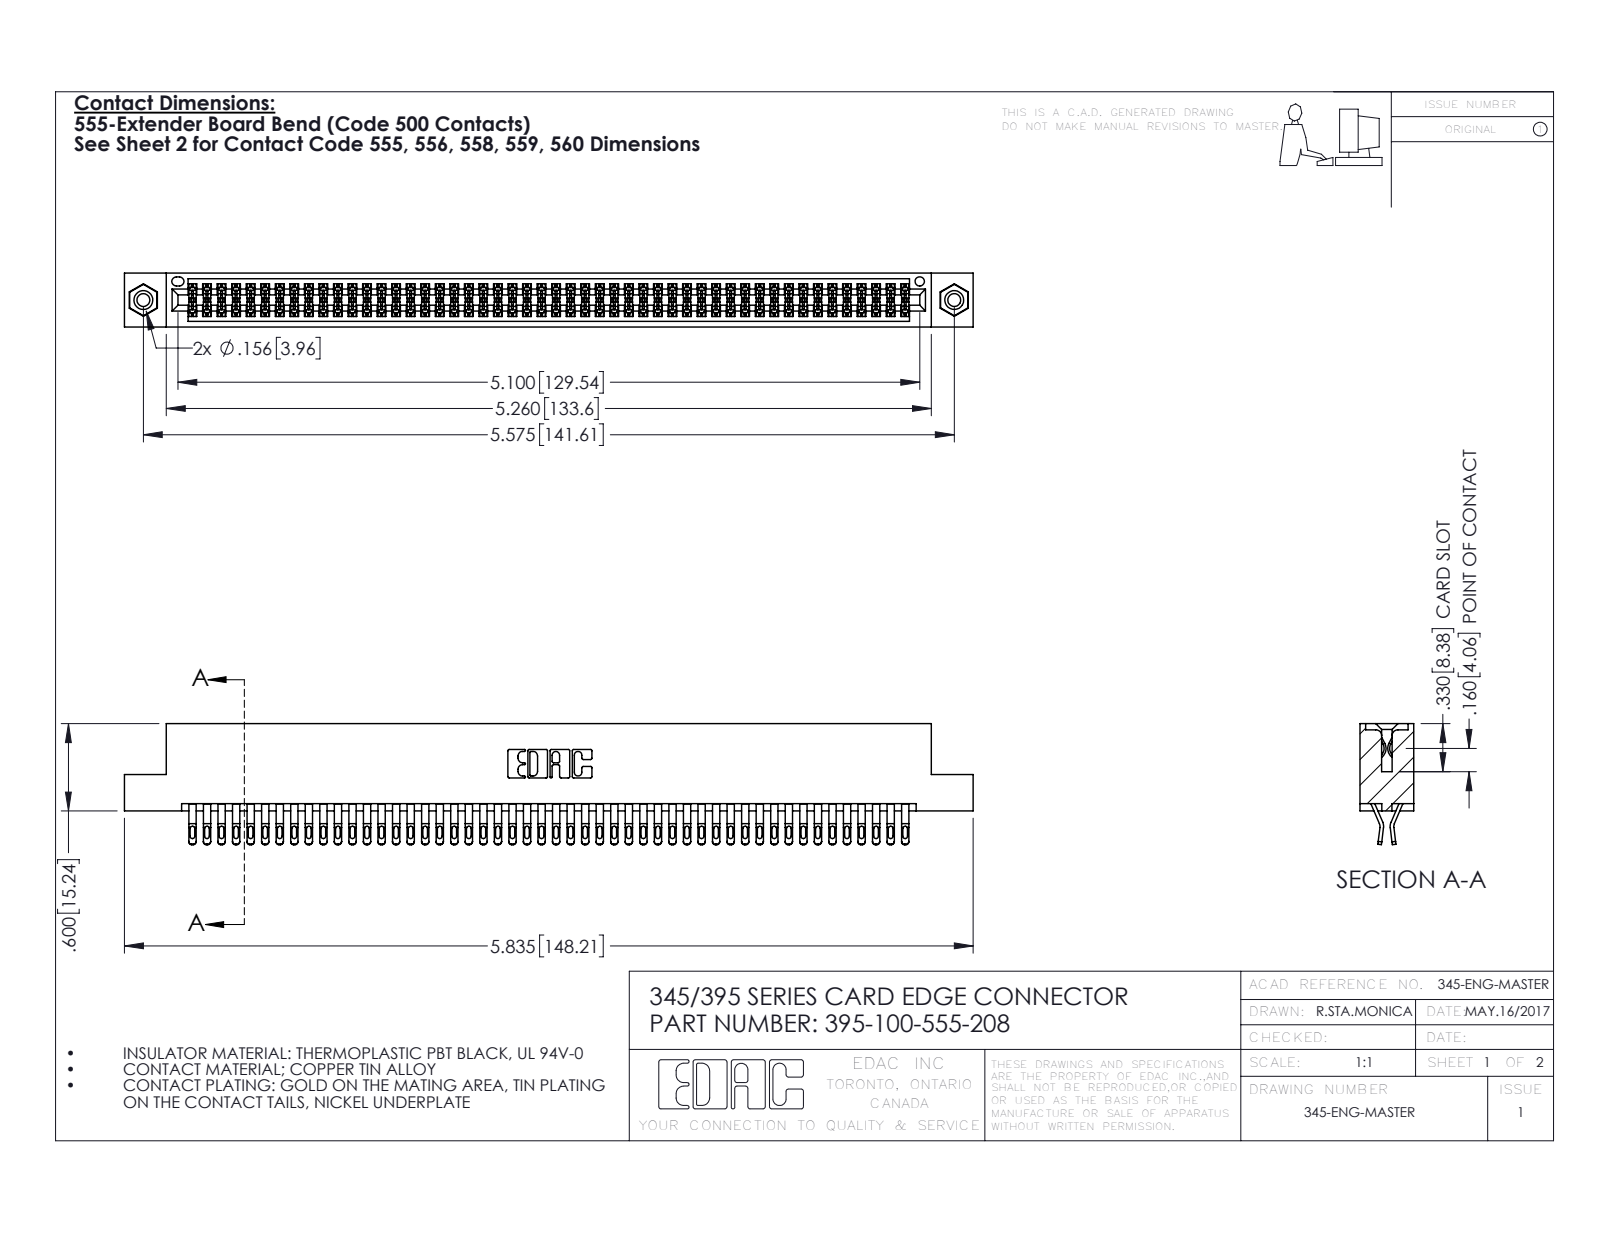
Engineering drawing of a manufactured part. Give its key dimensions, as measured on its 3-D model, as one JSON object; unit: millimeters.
{"part_name": "345 Part_Flush Mounting Lugs - 0.156 Dia-TI; 395-100-555-208; 345-250-001_345-250-003-102; 345-292-001_555 Tail", "step_written_by": "SolidWorks 2016 (CONFIG_CONTROL_DESIGN)", "units": "millimeters", "bodies": {"solids": 103, "faces": 5786, "planar": 3212, "cylindrical": 2558, "other": 16}, "overall_size": [148.2, 21.1, 9.4], "volume_mm3": 14700, "surface_area_mm2": 22990, "round_holes": [[2.3, 2], [3.2, 2], [4, 2], [1.6, 1]], "round_bosses_or_shafts": [[3.9, 2]], "partial_cylinders_radius": [[0.4, 250], [0.5, 200], [0.2, 150], [0.3, 22], [0.2, 6], [0.8, 6], [0.7, 3], [0.3, 2]], "face_to_face_distances": [1.8, 7.6, 0.6, 9.4, 5.1, 2.5, 6.9, 5.7, 4.4, 3.8], "hole_center_spacings": [6.9, 135.6, 141.6]}
